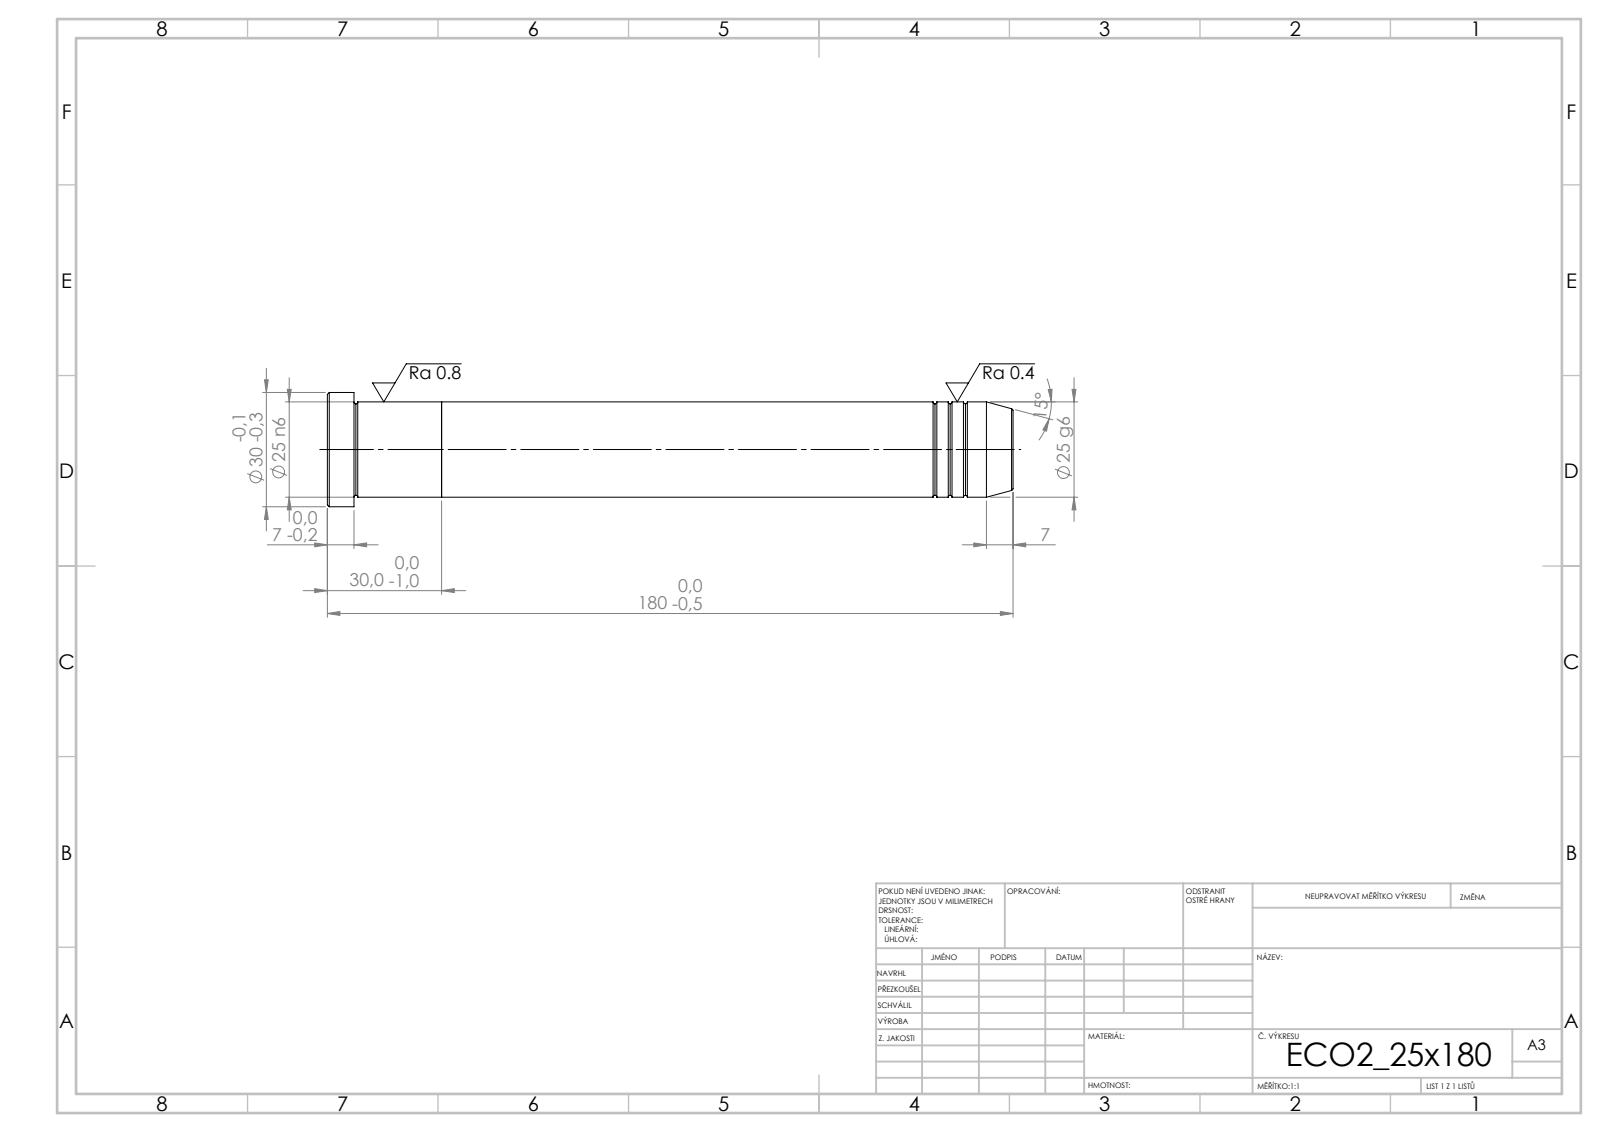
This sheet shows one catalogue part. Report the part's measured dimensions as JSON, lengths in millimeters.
{"step_written_by": "SolidWorks 2019 (CONFIG_CONTROL_DESIGN)", "units": "millimeters", "bodies": {"solids": 2, "faces": 39, "planar": 5, "cylindrical": 12, "other": 22}, "overall_size": [180, 30, 30], "volume_mm3": 89245, "surface_area_mm2": 16614, "round_bosses_or_shafts": [[30, 1], [25, 1]], "face_to_face_distances": [30, 150, 180, 173, 23, 7]}
